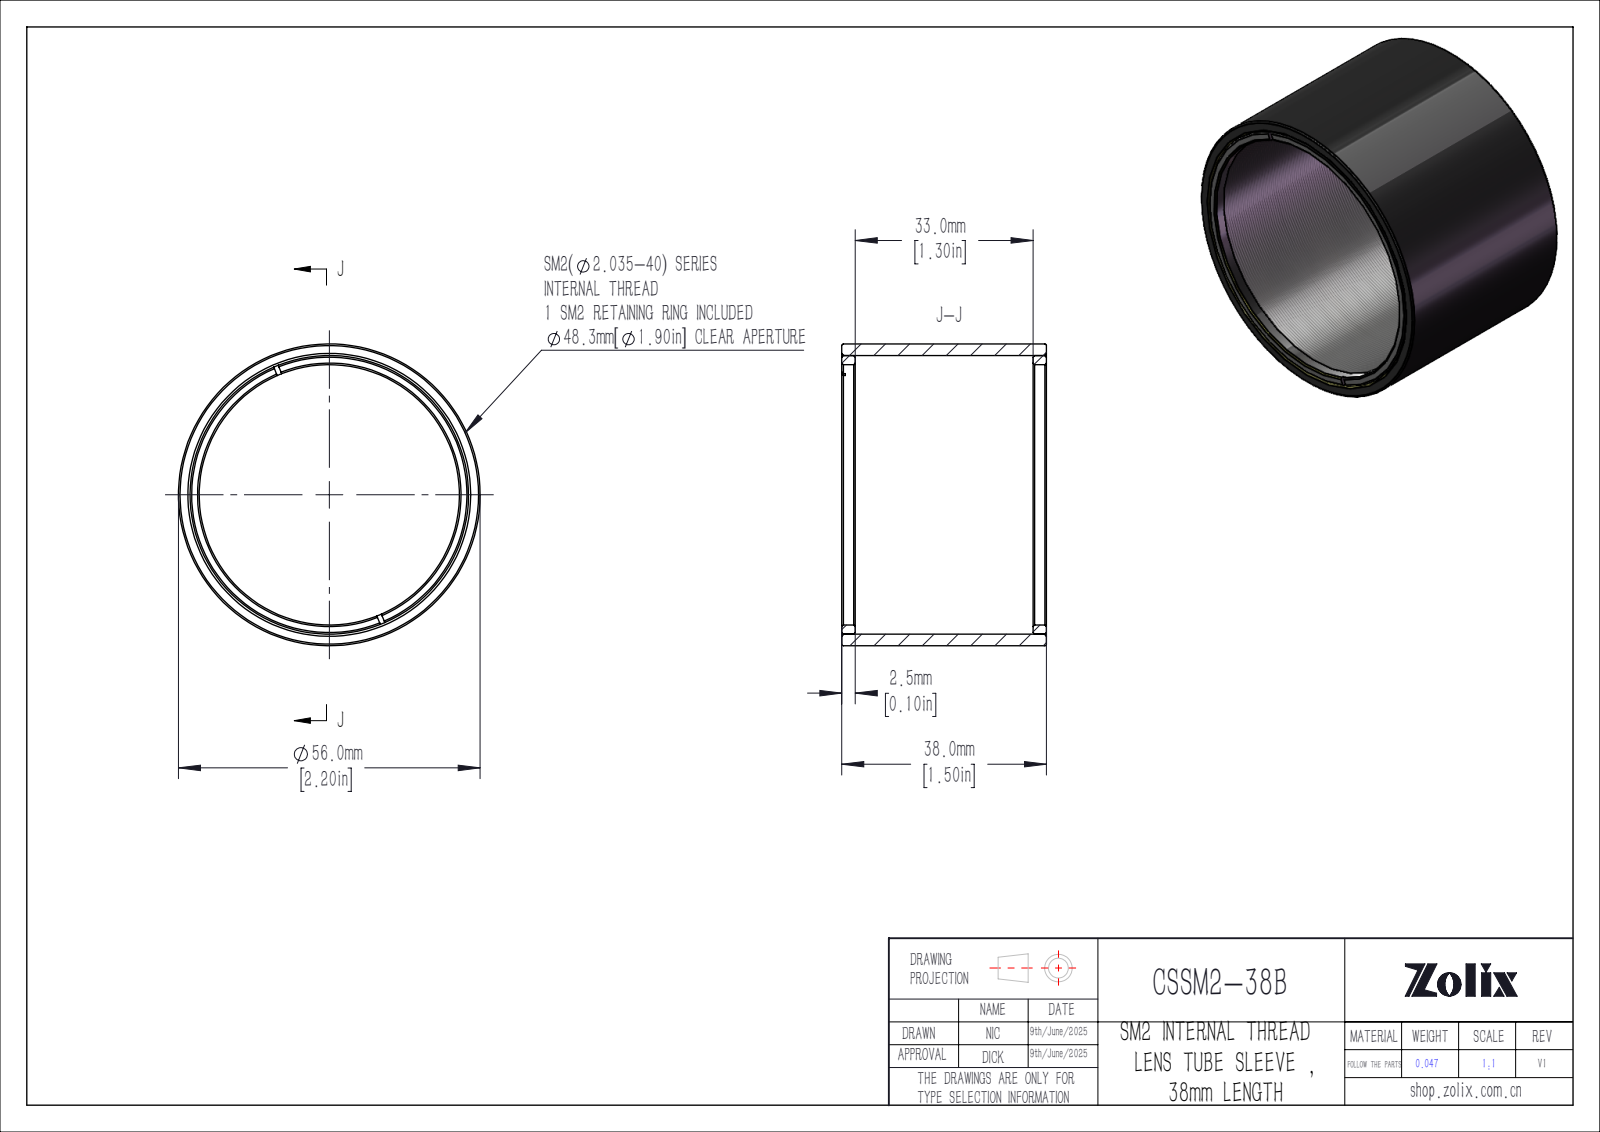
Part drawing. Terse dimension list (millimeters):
name: CSSM2-38B
written by: SolidWorks 2020 (CONFIG_CONTROL_DESIGN)
unit: mm
bodies: 3 solids, 374 faces (66 planar, 35 cylindrical, 273 other)
size: 56 × 56 × 38
volume: 15 090 mm³; area: 15 886 mm²
holes: 1× ⌀48.3
bosses: 1× ⌀56, 1× ⌀51.69
rounds: 1× R27.98
face distances: 38, 2.5, 35.5, 33, 1.85, 0.65, 37.35, 34.85, 0.9, 36.7
